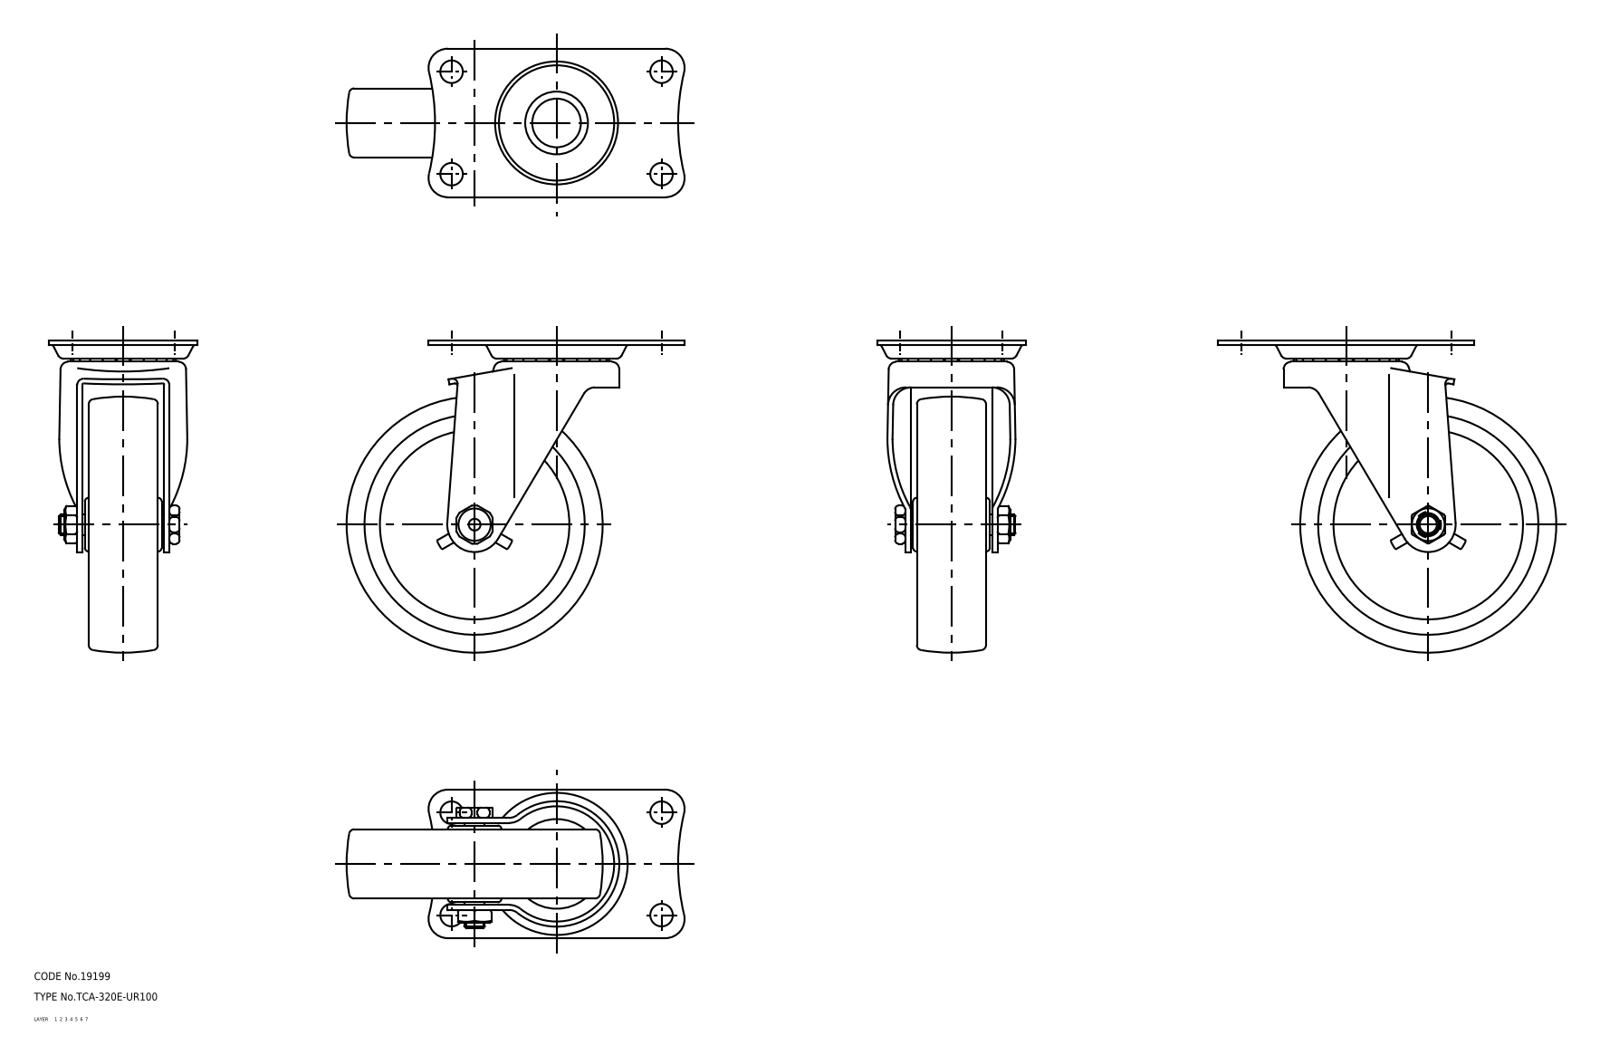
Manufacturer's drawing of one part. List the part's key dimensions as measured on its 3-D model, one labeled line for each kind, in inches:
Part name (STEP PRODUCT): wheel; mounting plate; main shaft; axle (+1 more)
STEP written by: CADfix (AUTOMOTIVE_DESIGN)
Units: inches
Bodies: 5 solids, 369 faces (0 planar, 0 cylindrical, 369 other)
Overall size (bounding box): 5.197 × 4.803 × 2.283
Volume: 12.22 in³ · Surface area: 96.37 in²
